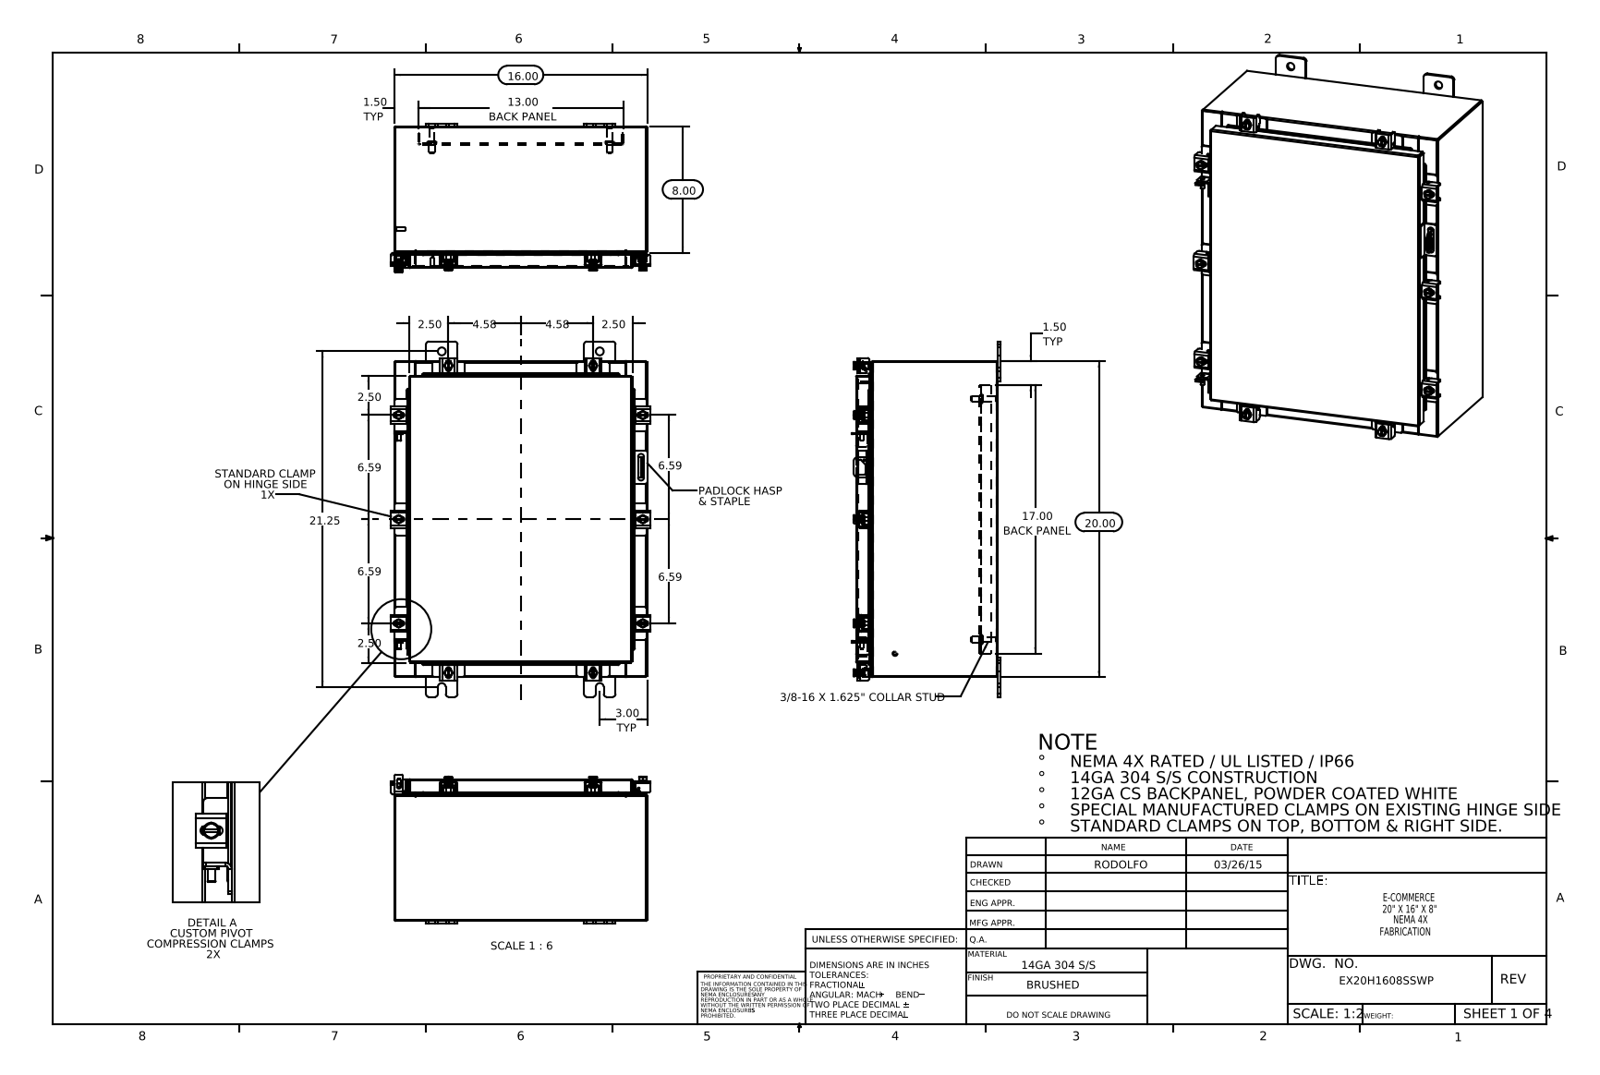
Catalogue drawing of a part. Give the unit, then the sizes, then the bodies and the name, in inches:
Units: inches
Overall size (bounding box): 22.5 × 16.421 × 9.453
Round holes (diameter × count): ⌀0.213 ×10, ⌀0.26 ×10, ⌀0.5 ×8, ⌀0.125 ×1, ⌀0.25 ×1
Round bosses / shafts (diameter × count): ⌀0.5 ×10, ⌀0.25 ×10, ⌀0.399 ×8, ⌀0.625 ×4, ⌀0.375 ×4, ⌀0.33 ×4, ⌀0.315 ×2, ⌀0.236 ×2
Partial cylindrical surfaces — rounded edges, fillets, slot ends (radius × count): R0.06 ×46, R0.013 ×24, R0.19 ×24, R0.088 ×22, R0.141 ×20, R0.12 ×18, R0.09 ×16, R0.1 ×16
Main face-to-face distances: 0.075, 8.9, 15.925, 8.975, 8.826, 19.925, 0.104, 1, 1.075, 7.826
Hole centre spacings: 2.347, 4.44, 6.594, 10.222, 12.696, 14.374, 15.683, 16.62
Volume: 135.4 in³ · Surface area: 3 406 in²
Bodies: 71 solids, 1784 faces (955 planar, 685 cylindrical, 144 other)
Part name (STEP PRODUCT): EX20H1608SSWP Standard Clamps; Clamp Top_RTP31; HW-CLN-NH-20320; N-WMT04X30402202210-00 22101002 (+8 more)
STEP written by: SolidWorks 2014 (CONFIG_CONTROL_DESIGN)
